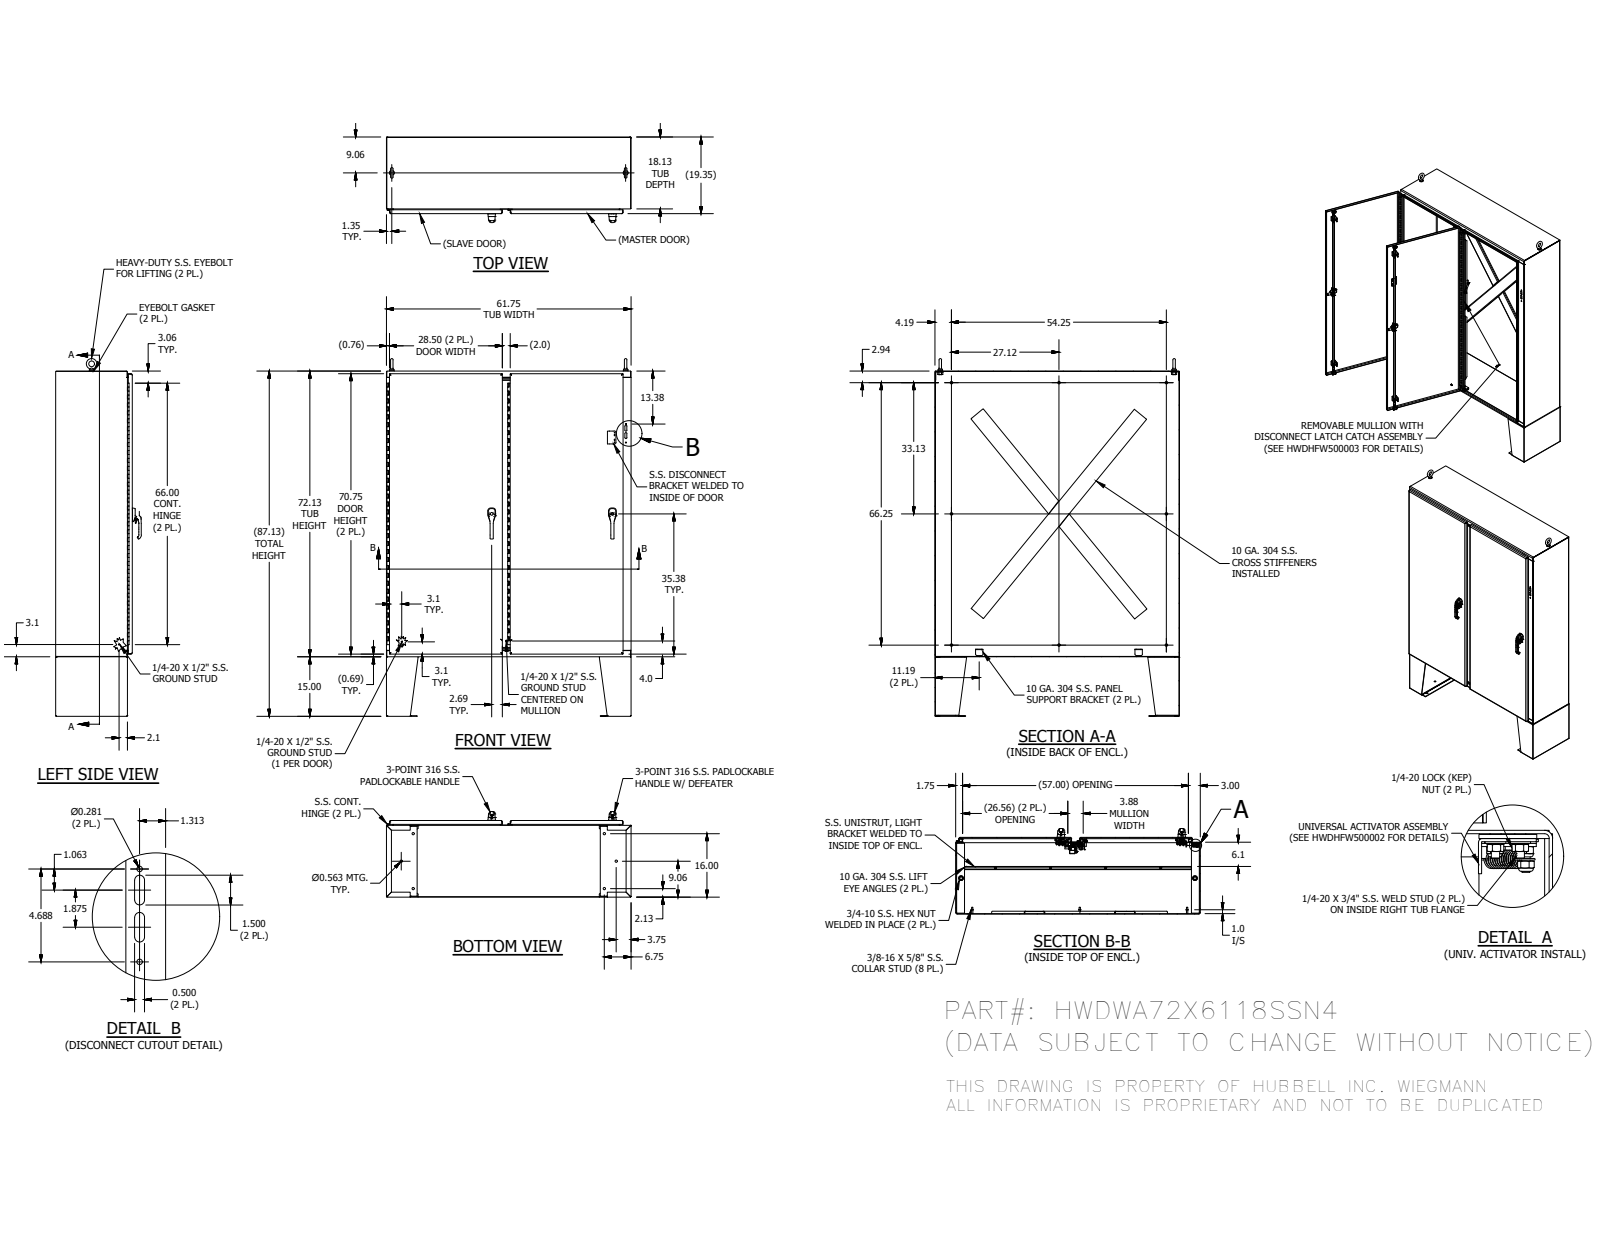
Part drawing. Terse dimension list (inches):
name: WA72X6118SSN4BLR; WAX6118SSN4TOP; WAX6118SSN4BTM; HFW332010S (+8 more)
written by: Autodesk Inventor 2016 (AUTOMOTIVE_DESIGN)
unit: in
bodies: 220 solids, 9194 faces (4286 planar, 3104 cylindrical, 1804 other)
size: 90.248 × 61.75 × 21.596
volume: 1 923 in³; area: 36 940 in²
holes: 18× ⌀0.375, 18× ⌀0.563, 17× ⌀0.25, 9× ⌀0.187, 8× ⌀0.19, 8× ⌀0.196, 8× ⌀0.262, 8× ⌀0.289, 8× ⌀0.335, 8× ⌀0.38, 6× ⌀0.156, 6× ⌀0.213
bosses: 20× ⌀0.25, 18× ⌀0.33, 13× ⌀0.625, 12× ⌀0.337, 11× ⌀0.375, 9× ⌀0.563, 8× ⌀0.28, 6× ⌀1
rounds: 359× R0.02, 221× R0.012, 192× R0.02, 55× R0.125, 42× R0.019, 28× R0.05, 28× R0.079, 23× R0.25
face distances: 0.104, 19.244, 19.14, 19.348, 61.646, 72.021, 61.542, 61.75, 18.021, 1.223
hole spacings: 0.38, 0.76, 1.195, 1.459, 4.963, 5, 6.845, 7.469
